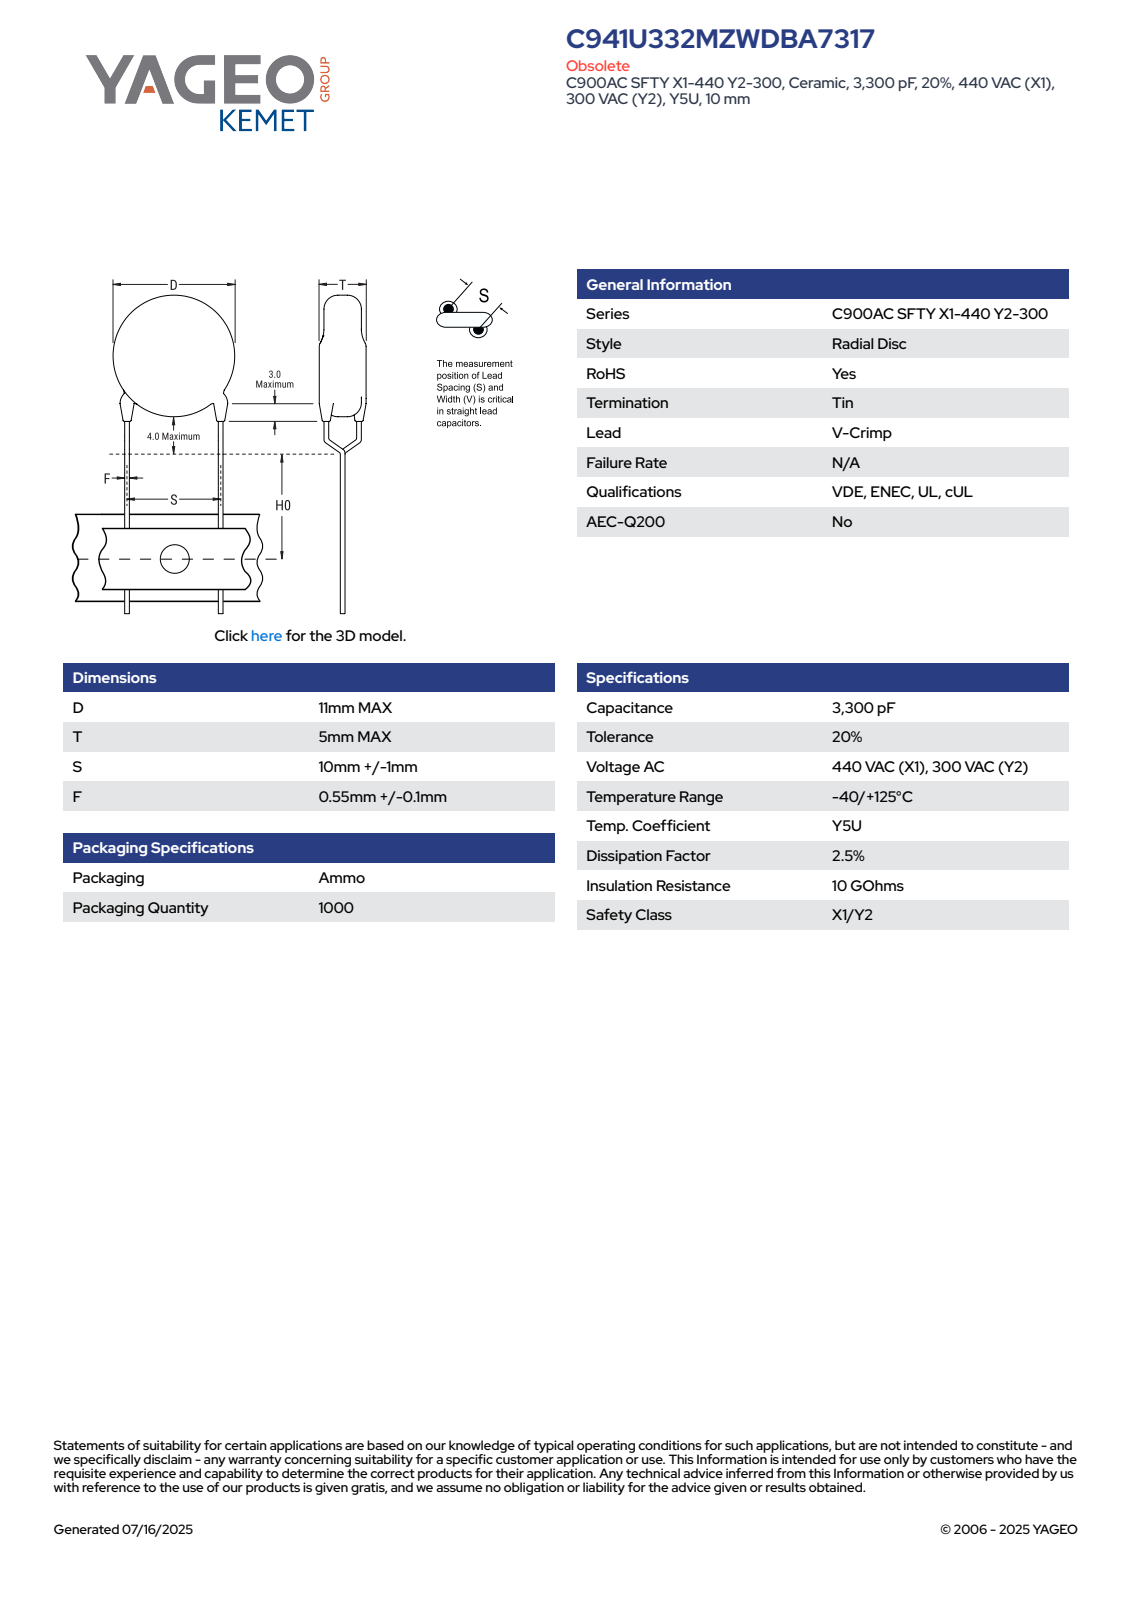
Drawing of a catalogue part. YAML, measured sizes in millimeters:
part_name: "CCD_VCC900_D11T5S10LL20F0.65"
step_written_by: "SolidWorks 2014 (AUTOMOTIVE_DESIGN)"
units: millimeters
bodies: {solids: 5, faces: 93, planar: 65, cylindrical: 16, other: 12}
overall_size: [34.8, 11, 5]
volume: 481
surface_area: 456
round_bosses_or_shafts:
  - {diameter: 0.65, count: 6}
  - {diameter: 11, count: 1}
face_to_face_distances: [5, 22.9, 30.01, 7.11, 28.58, 5.68, 1.43, 0.39, 0.35, 5.84]
